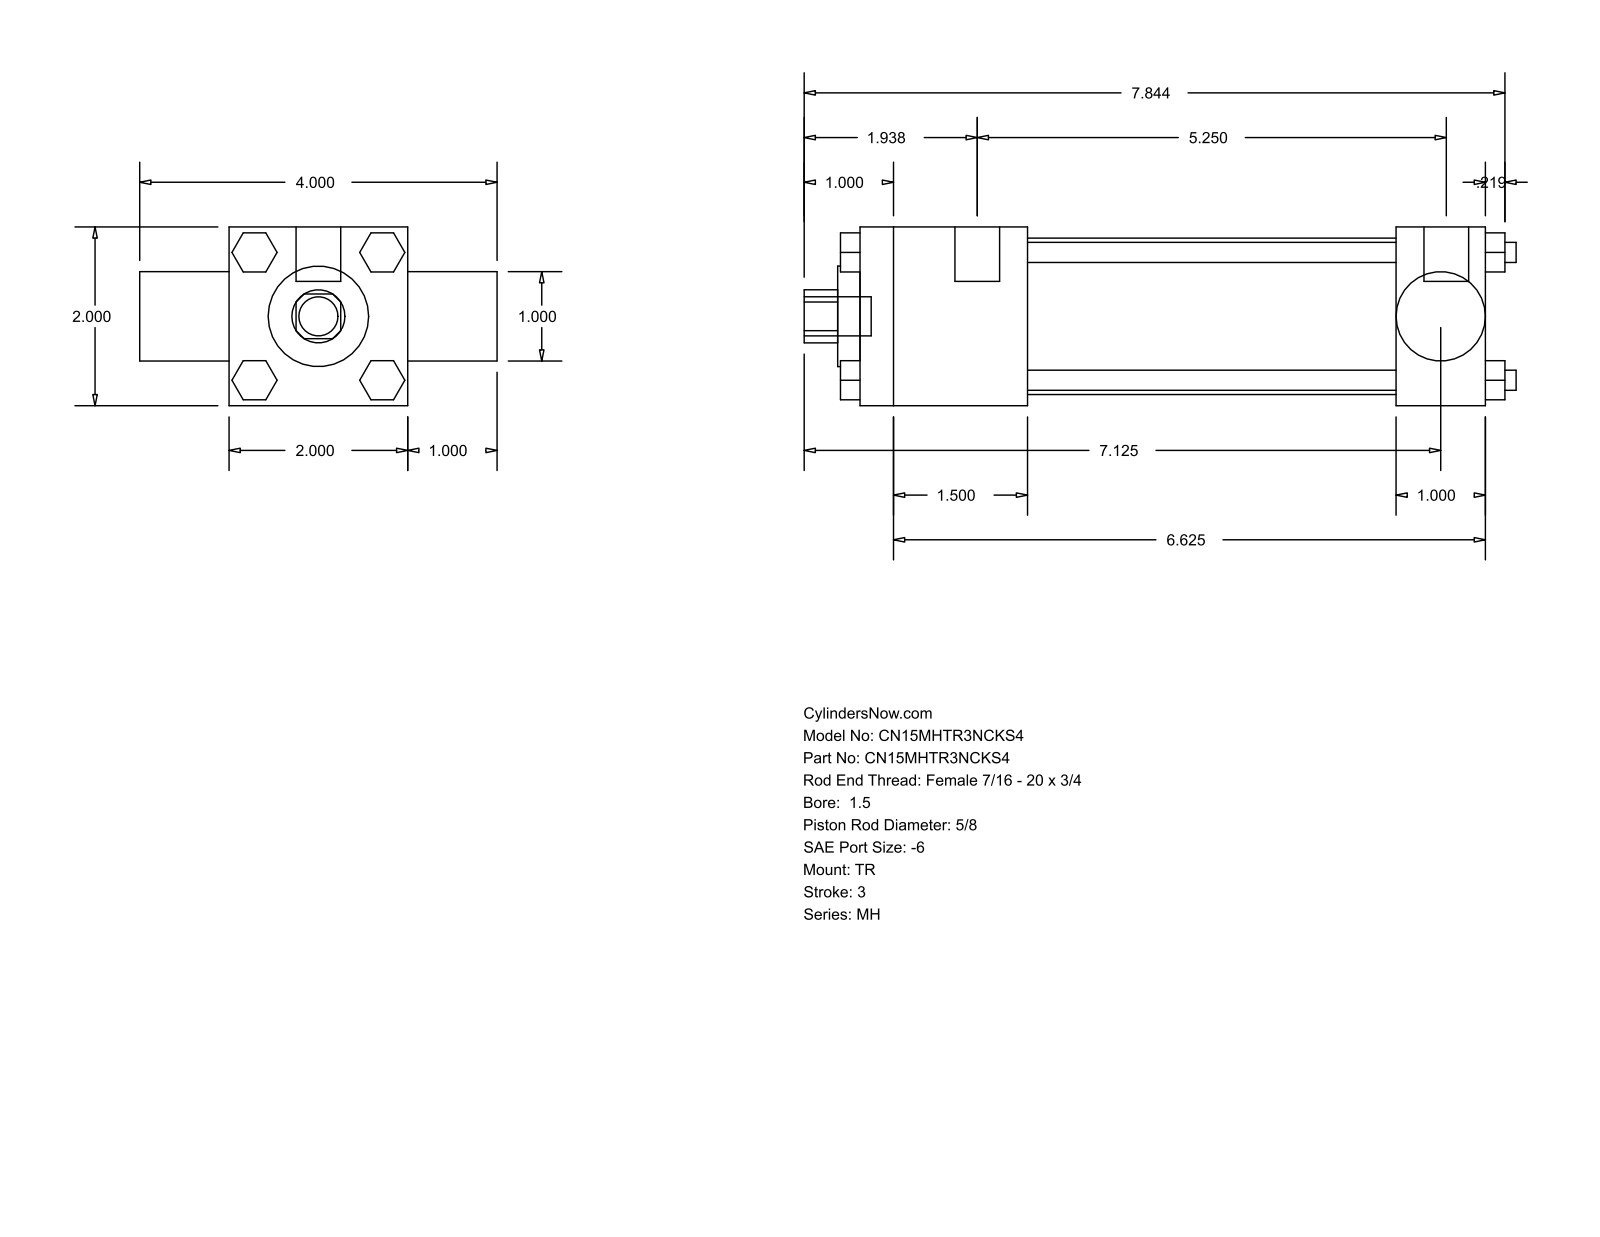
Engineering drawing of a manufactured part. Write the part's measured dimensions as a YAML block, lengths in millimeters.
part_name: "MH_TR__0150_0.625"
step_written_by: "GSSL Pune (CONFIG_CONTROL_DESIGN)"
units: millimeters
bodies: {solids: 0, faces: 120, planar: 92, cylindrical: 28, other: 0}
overall_size: [202.41, 101.6, 50.8]
round_holes:
  - {diameter: 15.88, count: 1}
  - {diameter: 25.35, count: 1}
  - {diameter: 28.57, count: 1}
  - {diameter: 44.45, count: 1}
round_bosses_or_shafts:
  - {diameter: 5.71, count: 4}
  - {diameter: 5.56, count: 3}
  - {diameter: 12.7, count: 2}
  - {diameter: 11.11, count: 1}
partial_cylinders:
  - {radius: 7.54, count: 1}
face_to_face_distances: [50.8, 25.4, 177.8, 76.2, 47.62, 130.18, 152.4, 104.78, 11.11, 18.16]
